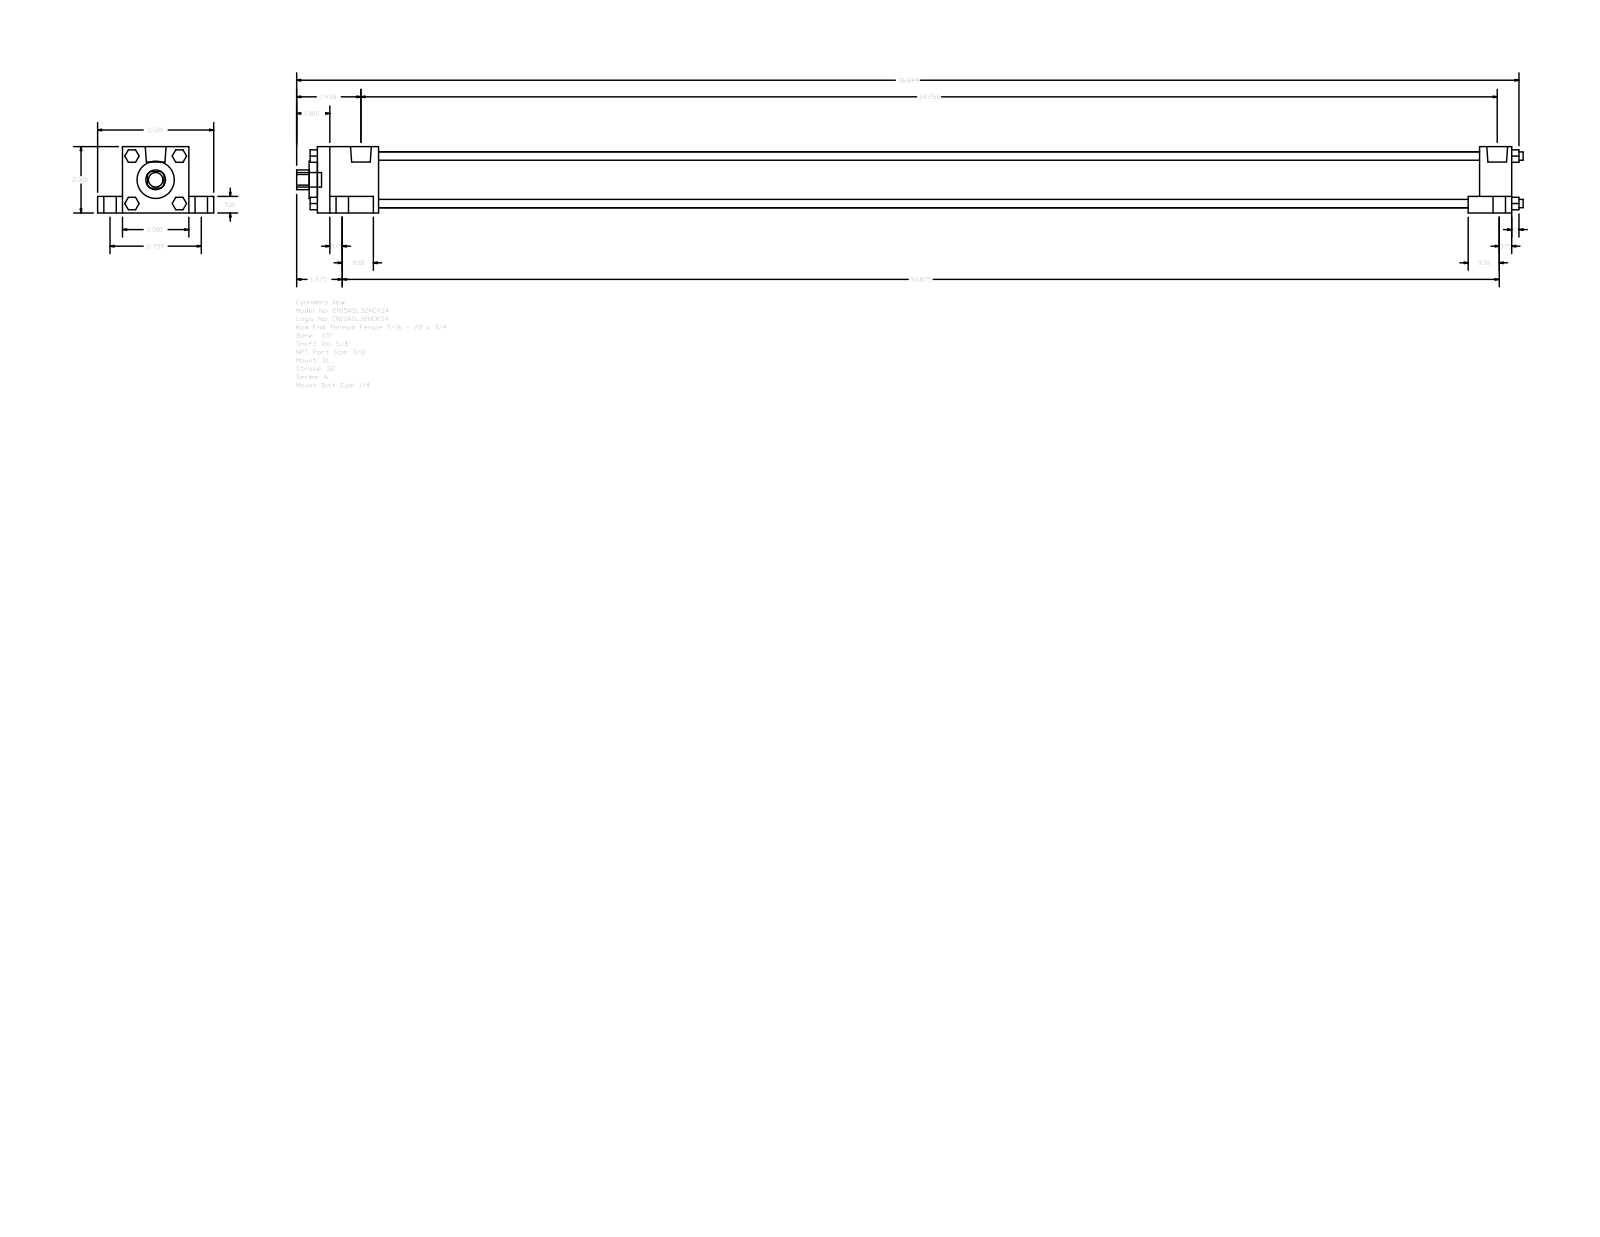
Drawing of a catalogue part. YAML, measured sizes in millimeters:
part_name: "A_SL__0150_0.625"
step_written_by: "GSSL Pune (CONFIG_CONTROL_DESIGN)"
units: millimeters
bodies: {solids: 0, faces: 148, planar: 112, cylindrical: 36, other: 0}
overall_size: [939.01, 88.9, 50.8]
round_holes:
  - {diameter: 15.88, count: 1}
  - {diameter: 28.57, count: 1}
  - {diameter: 42.93, count: 1}
round_bosses_or_shafts:
  - {diameter: 15.88, count: 4}
  - {diameter: 9.53, count: 4}
  - {diameter: 6.35, count: 4}
  - {diameter: 5.56, count: 4}
  - {diameter: 15.93, count: 2}
  - {diameter: 11.11, count: 1}
partial_cylinders:
  - {radius: 7.54, count: 1}
face_to_face_distances: [50.8, 19.05, 12.7, 38.1, 69.85, 914.39, 9.52, 889.79, 24.6, 46.83]
